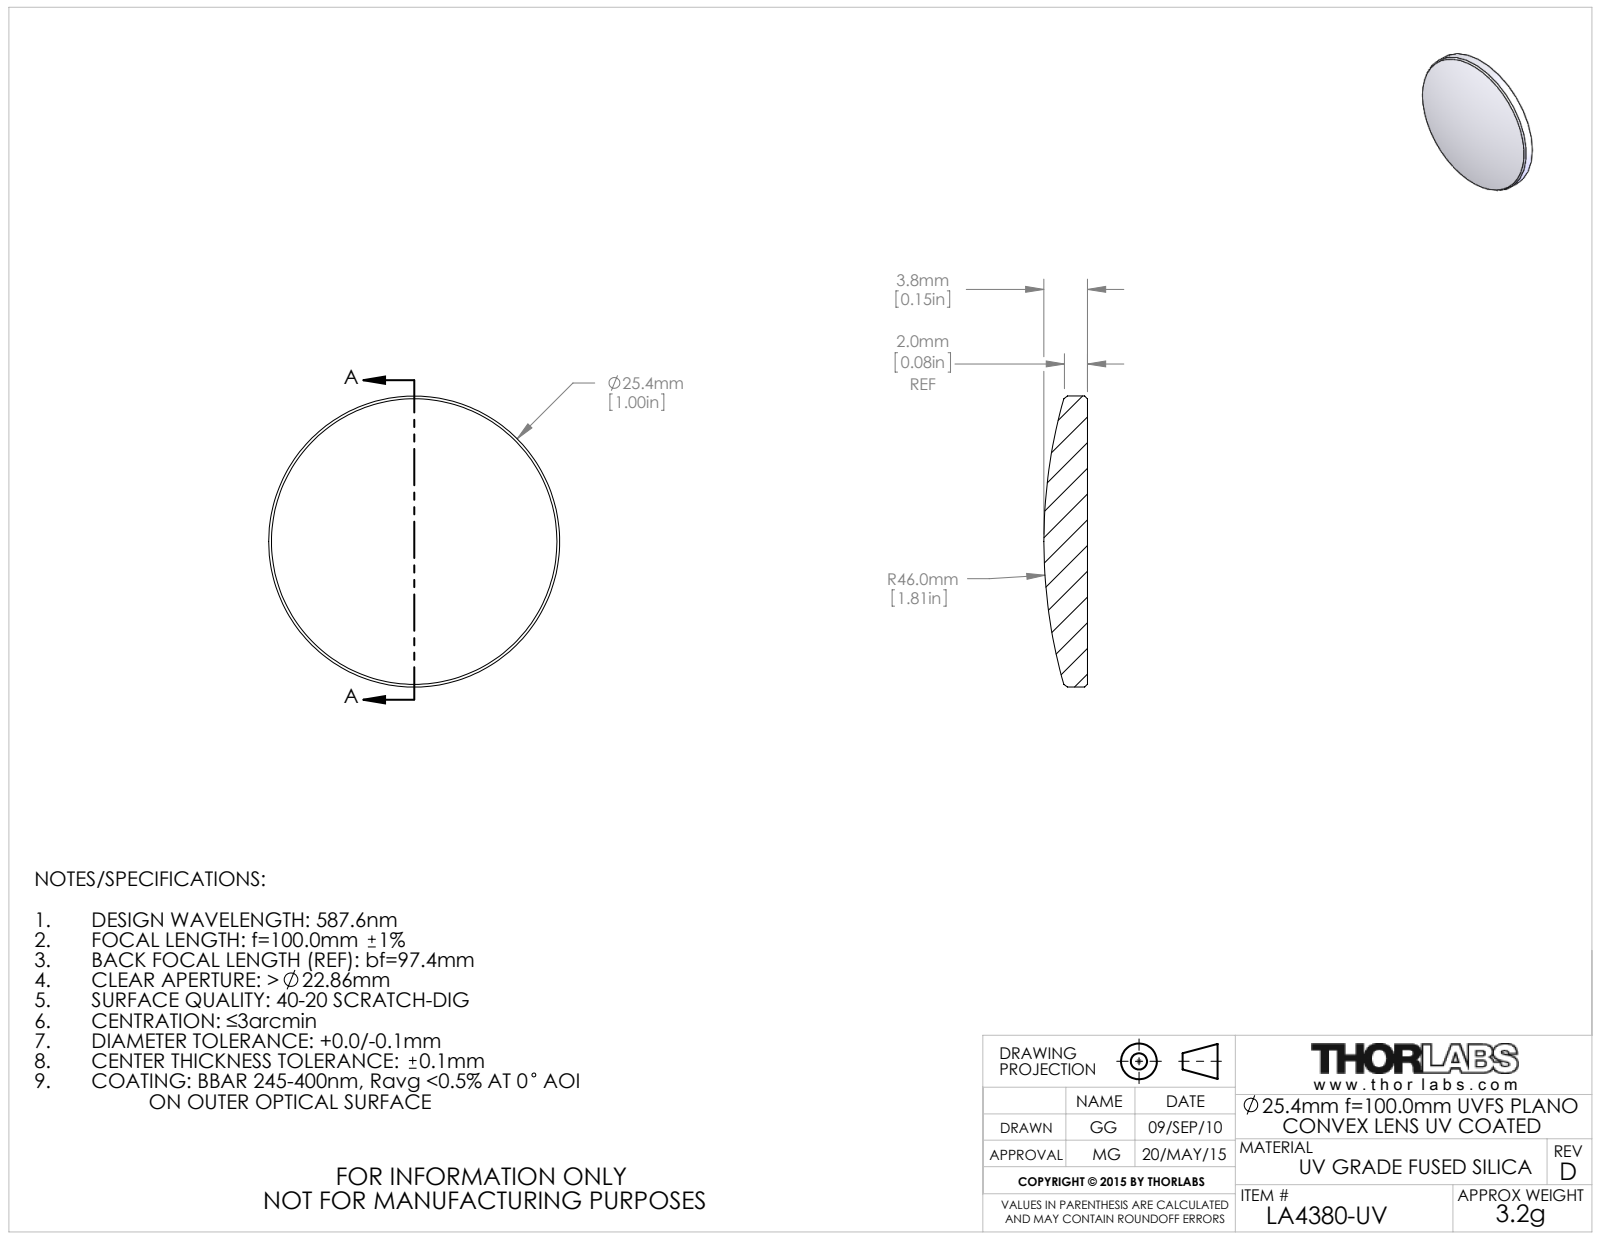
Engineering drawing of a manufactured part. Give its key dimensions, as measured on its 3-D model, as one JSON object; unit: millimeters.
{"part_name": "4282-E0W", "step_written_by": "SolidWorks 2014 (CONFIG_CONTROL_DESIGN)", "units": "millimeters", "bodies": {"solids": 1, "faces": 9, "planar": 1, "cylindrical": 2, "other": 6}, "overall_size": [25.4, 25.4, 3.8], "volume_mm3": 1467, "surface_area_mm2": 1163, "round_bosses_or_shafts": [[25.4, 1]]}
